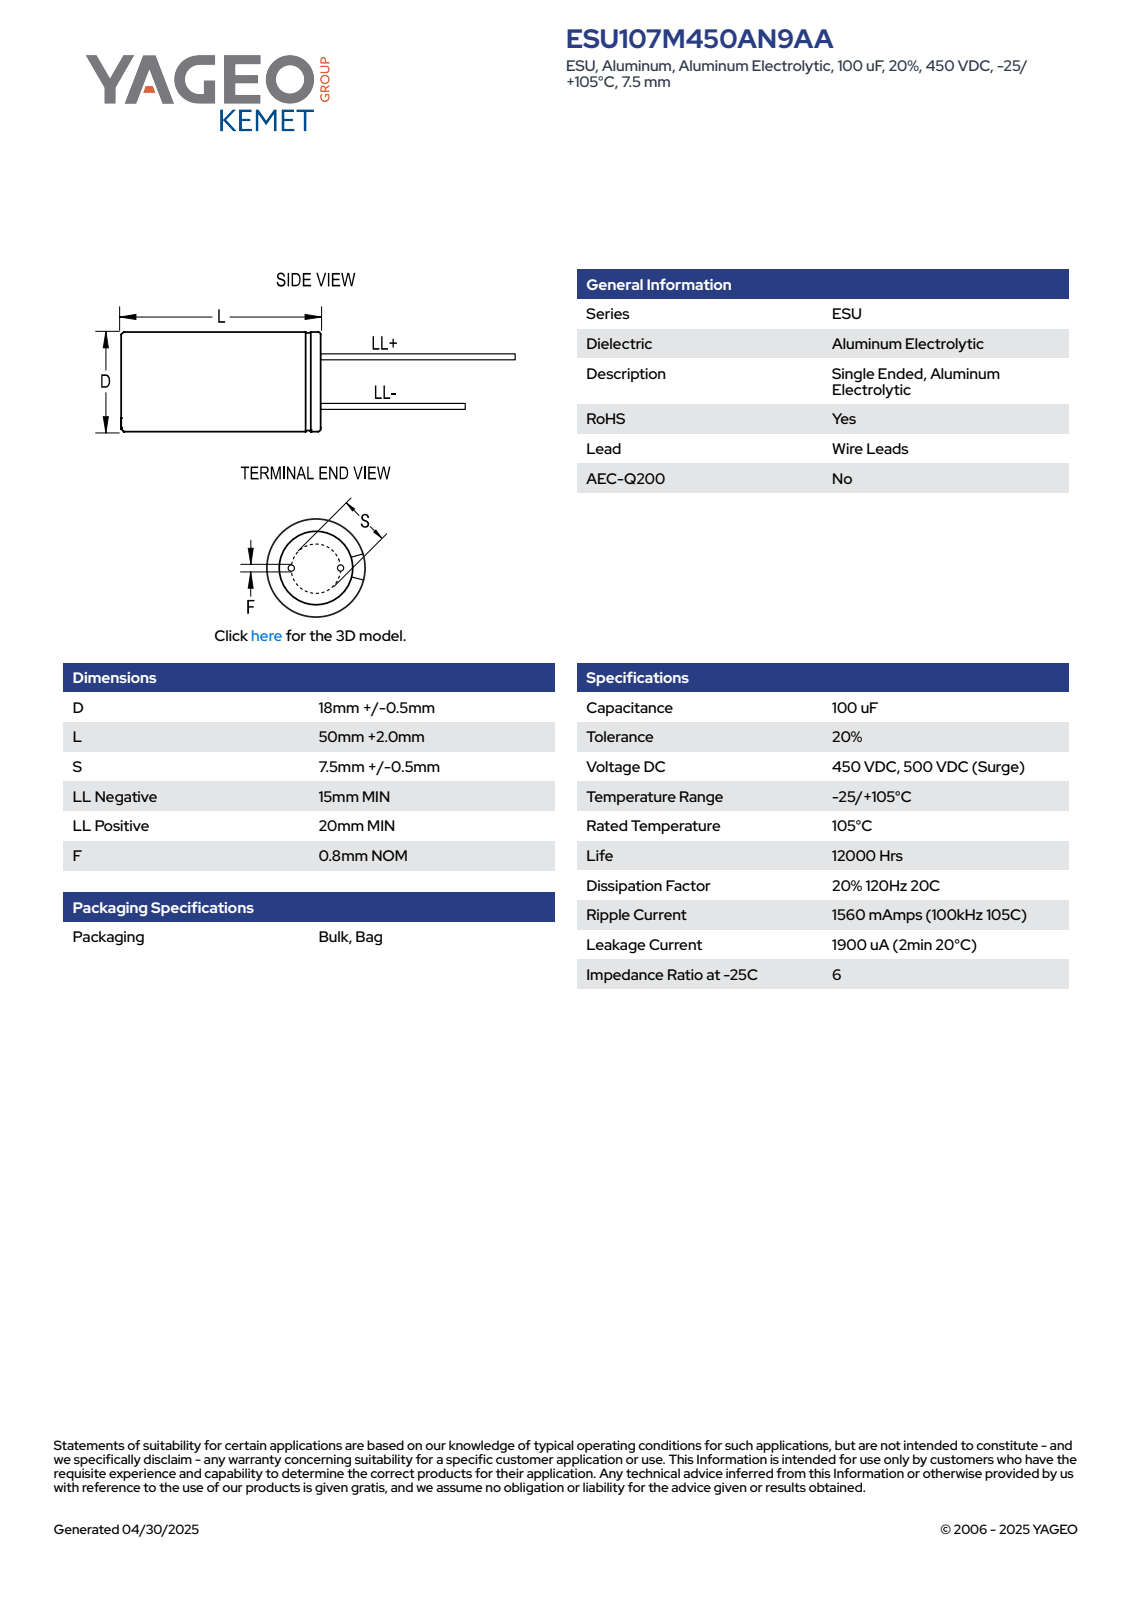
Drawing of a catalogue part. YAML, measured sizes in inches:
part_name: "CAR_KLP_18X50_D18.5L52S7.5F0.8"
step_written_by: "SolidWorks 2014 (AUTOMOTIVE_DESIGN)"
units: inches
bodies: {solids: 4, faces: 75, planar: 61, cylindrical: 8, other: 6}
overall_size: [2.835, 0.728, 0.728]
volume: 0.85
surface_area: 5.778
round_bosses_or_shafts:
  - {diameter: 0.031, count: 2}
  - {diameter: 0.728, count: 1}
face_to_face_distances: [2.047, 2.048, 2.638, 2.835, 2.638, 2.835, 0.591, 0.787, 0.197, 0.098]
